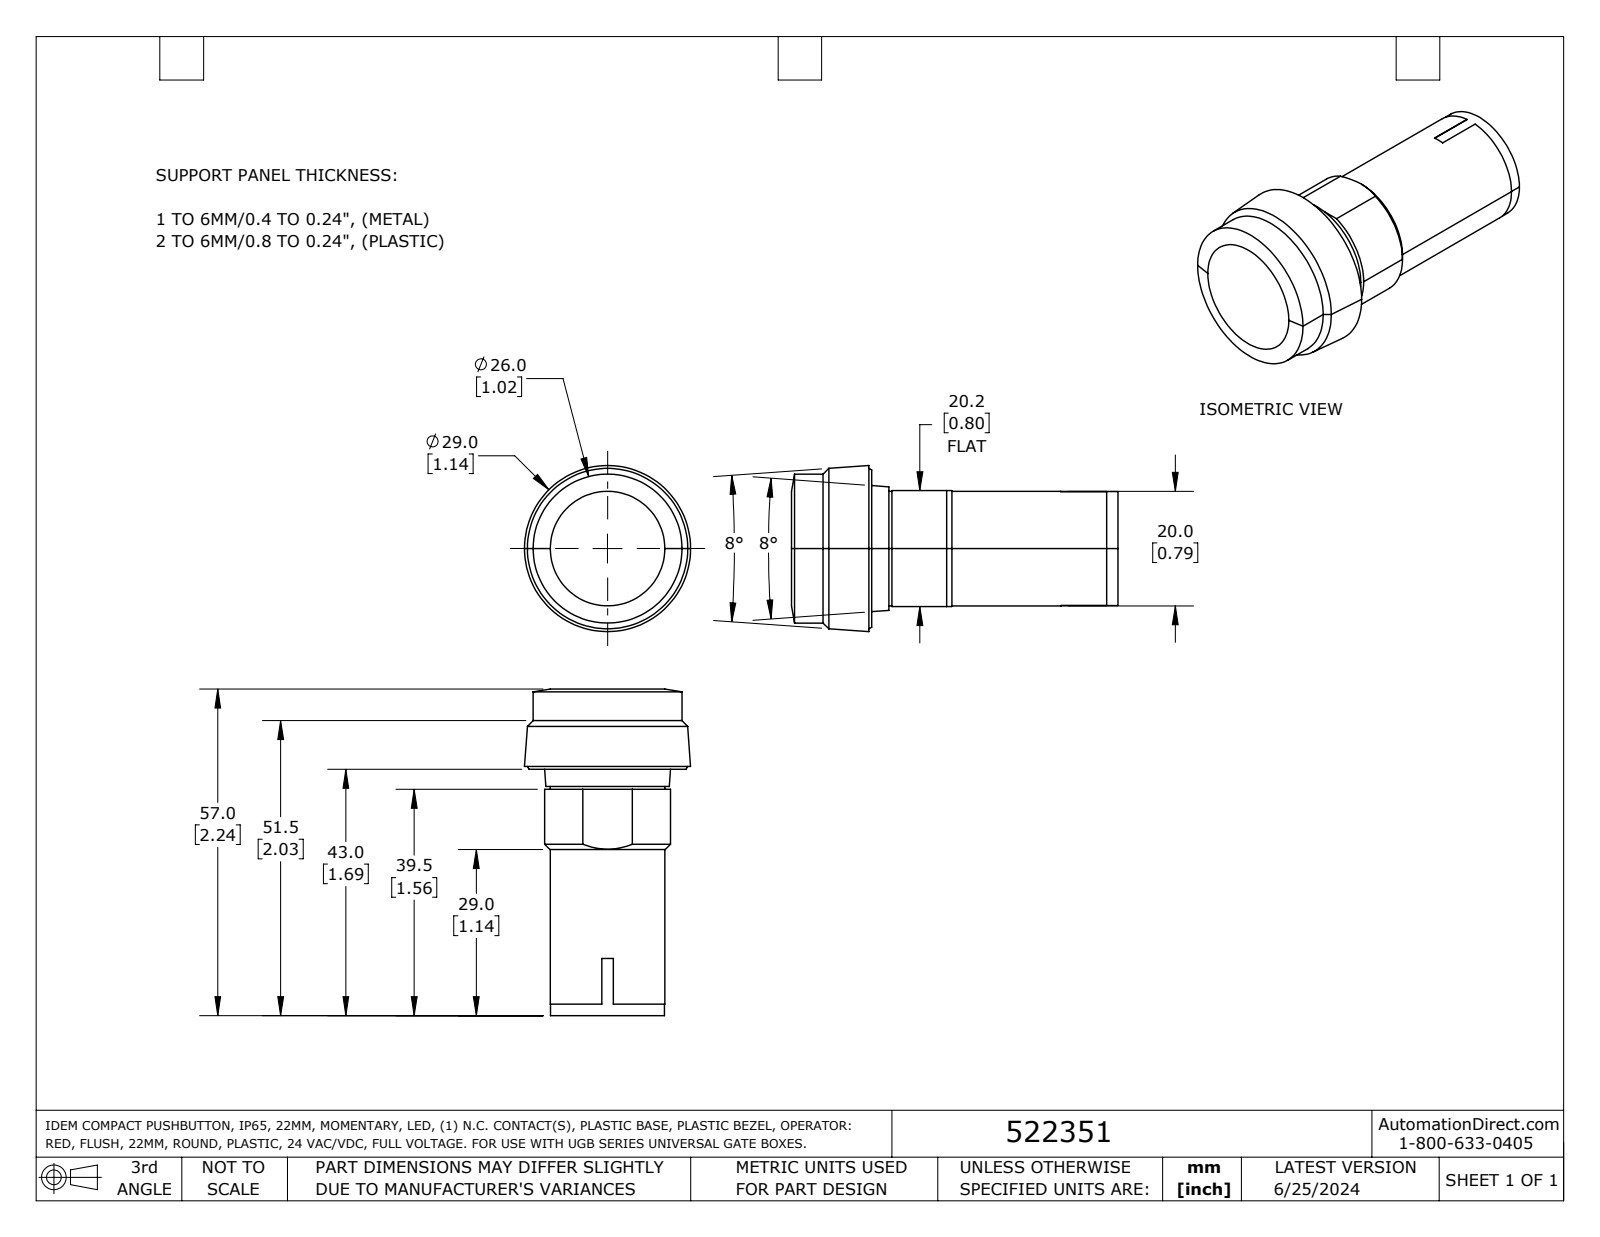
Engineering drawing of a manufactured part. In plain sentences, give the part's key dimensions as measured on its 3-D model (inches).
The part is named "522351". Its 3-D file was written by "SolidWorks 2023 (AUTOMOTIVE_DESIGN)". It is 1 solid with 41 faces: 17 planar, 12 cylindrical and 12 other. Overall it measures 2.244 by 1.142 by 1.142 inches. Its volume is 1.37 cubic inches and its surface area 8.094 square inches. Round bosses or shafts: 1 of diameter 1.024, 1 of diameter 0.787, 1 of diameter 0.783. Partial cylindrical surfaces (rounded edges, fillets, slot ends): 1 of radius 0.433. The main face-to-face distances are 2.244, 0.551, 1.693, 0.138, 0.02, 0.797, 0.689, 1.555, 0.669, 0.118.
